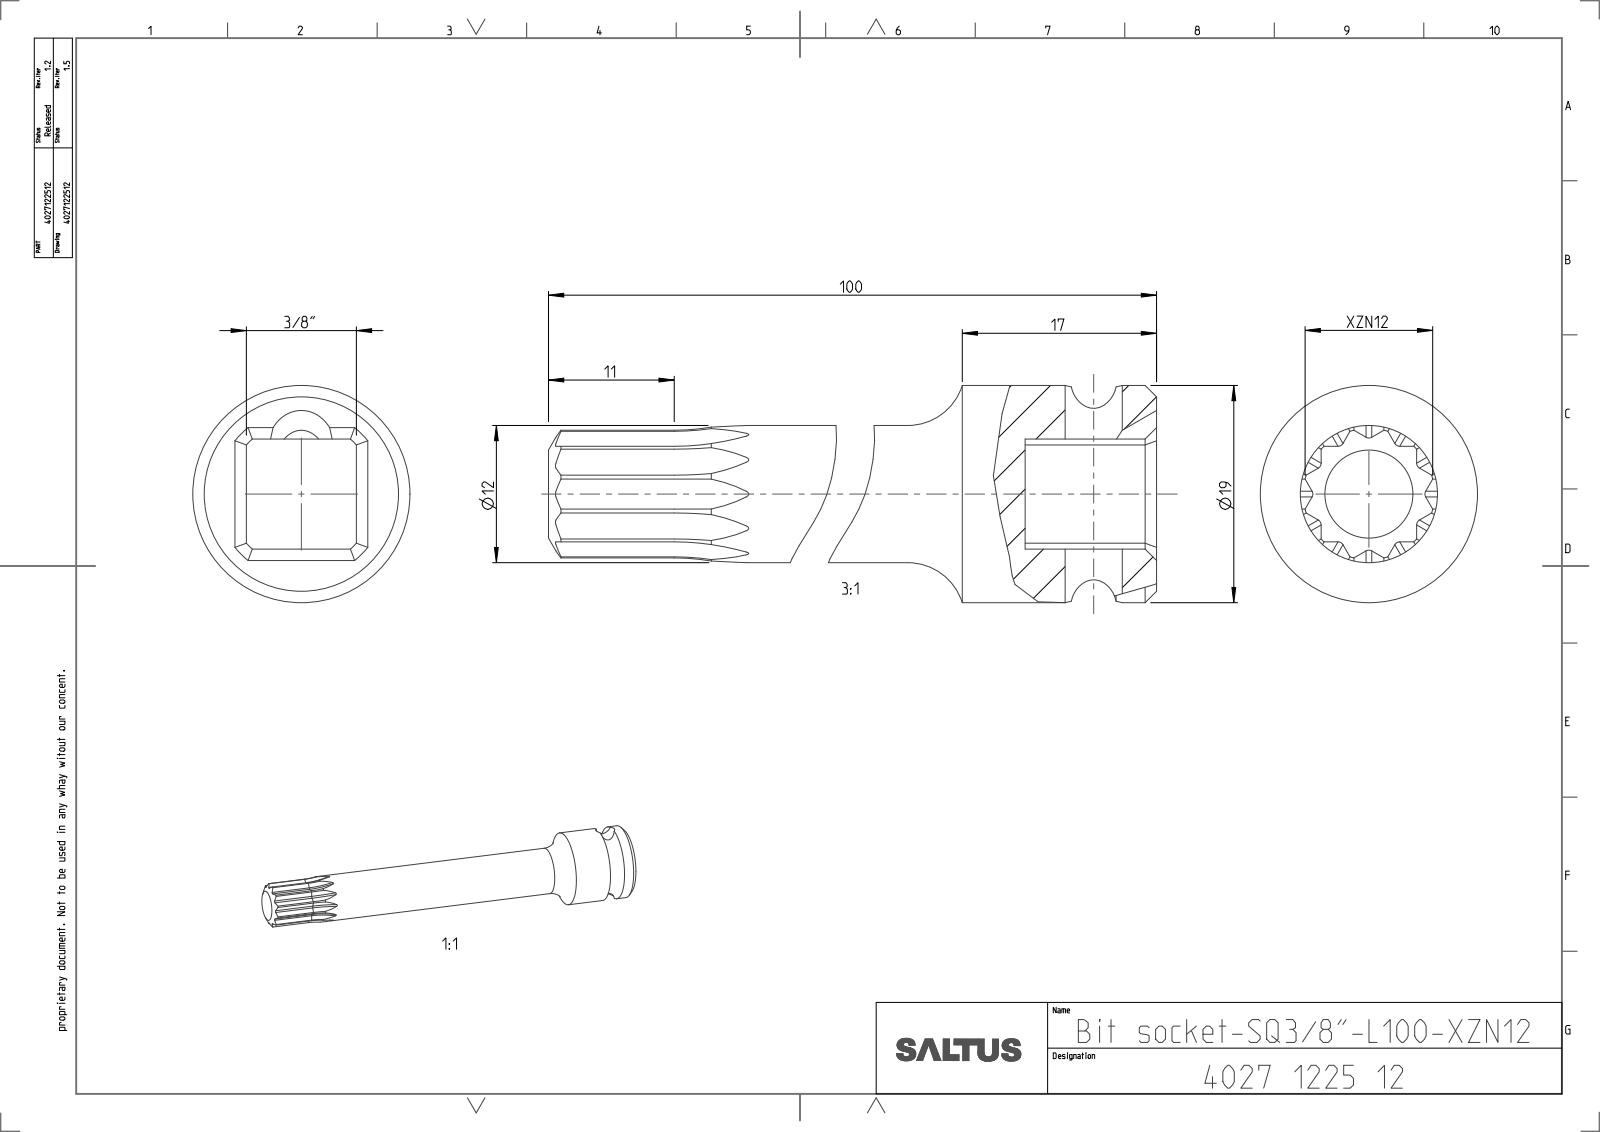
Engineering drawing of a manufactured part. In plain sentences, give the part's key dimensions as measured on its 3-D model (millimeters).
The part is named "4027122512". Its 3-D file was written by "CREO PARAMETRIC BY PTC INC, 2022414 (CONFIG_CONTROL_DESIGN)". It is 1 solid with 135 faces: 36 planar, 39 cylindrical and 60 other. Overall it measures 100 by 19 by 19 millimeters. Its volume is 12 497 cubic millimeters and its surface area 5 097 square millimeters. Round holes: 1 of diameter 5. Round bosses or shafts: 1 of diameter 19, 1 of diameter 12. Partial cylindrical surfaces (rounded edges, fillets, slot ends): 12 of radius 0.5, 1 of radius 3, 1 of radius 5.74, 1 of radius 6.45. The main face-to-face distances are 9.62, 8.36, 0.63, 8.99, 11.5, 100, 88.5.
